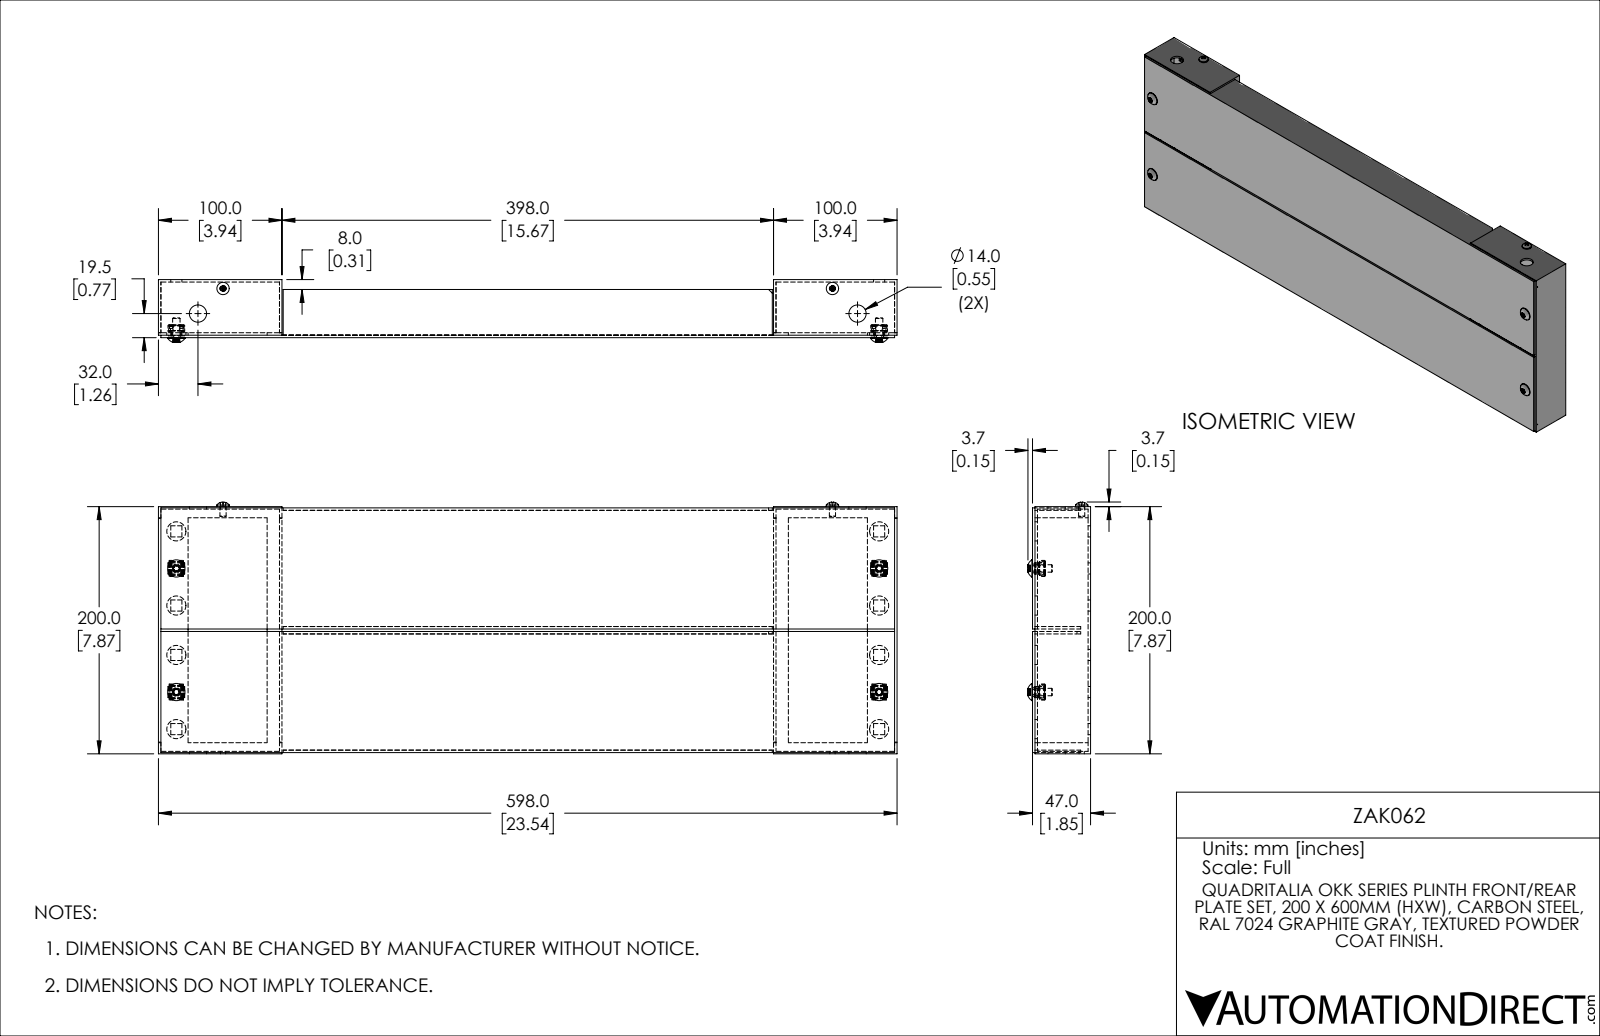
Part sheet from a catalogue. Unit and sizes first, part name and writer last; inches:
Units: inches
Overall size (bounding box): 23.543 × 8.021 × 1.996
Round holes (diameter × count): ⌀0.61 ×8, ⌀0.276 ×4, ⌀0.167 ×2, ⌀0.194 ×2, ⌀0.194 ×2, ⌀0.551 ×2
Round bosses / shafts (diameter × count): ⌀0.551 ×4, ⌀0.236 ×4, ⌀0.394 ×2, ⌀0.197 ×2
Partial cylindrical surfaces — rounded edges, fillets, slot ends (radius × count): R0.02 ×68, R0.01 ×48, R0.039 ×20
Main face-to-face distances: 0.079, 3.858, 3.937, 1.772, 3.78, 1.693, 0.039, 0.157, 1.85, 7.717
Hole centre spacings: 1.181, 22.433, 3.937, 22.402, 22.745, 2.362, 2.756, 5.118
Volume: 34.15 in³ · Surface area: 887.5 in²
Bodies: 18 solids, 742 faces (466 planar, 252 cylindrical, 24 other)
Part name (STEP PRODUCT): ZAK062
STEP written by: SolidWorks 2021 (CONFIG_CONTROL_DESIGN)
